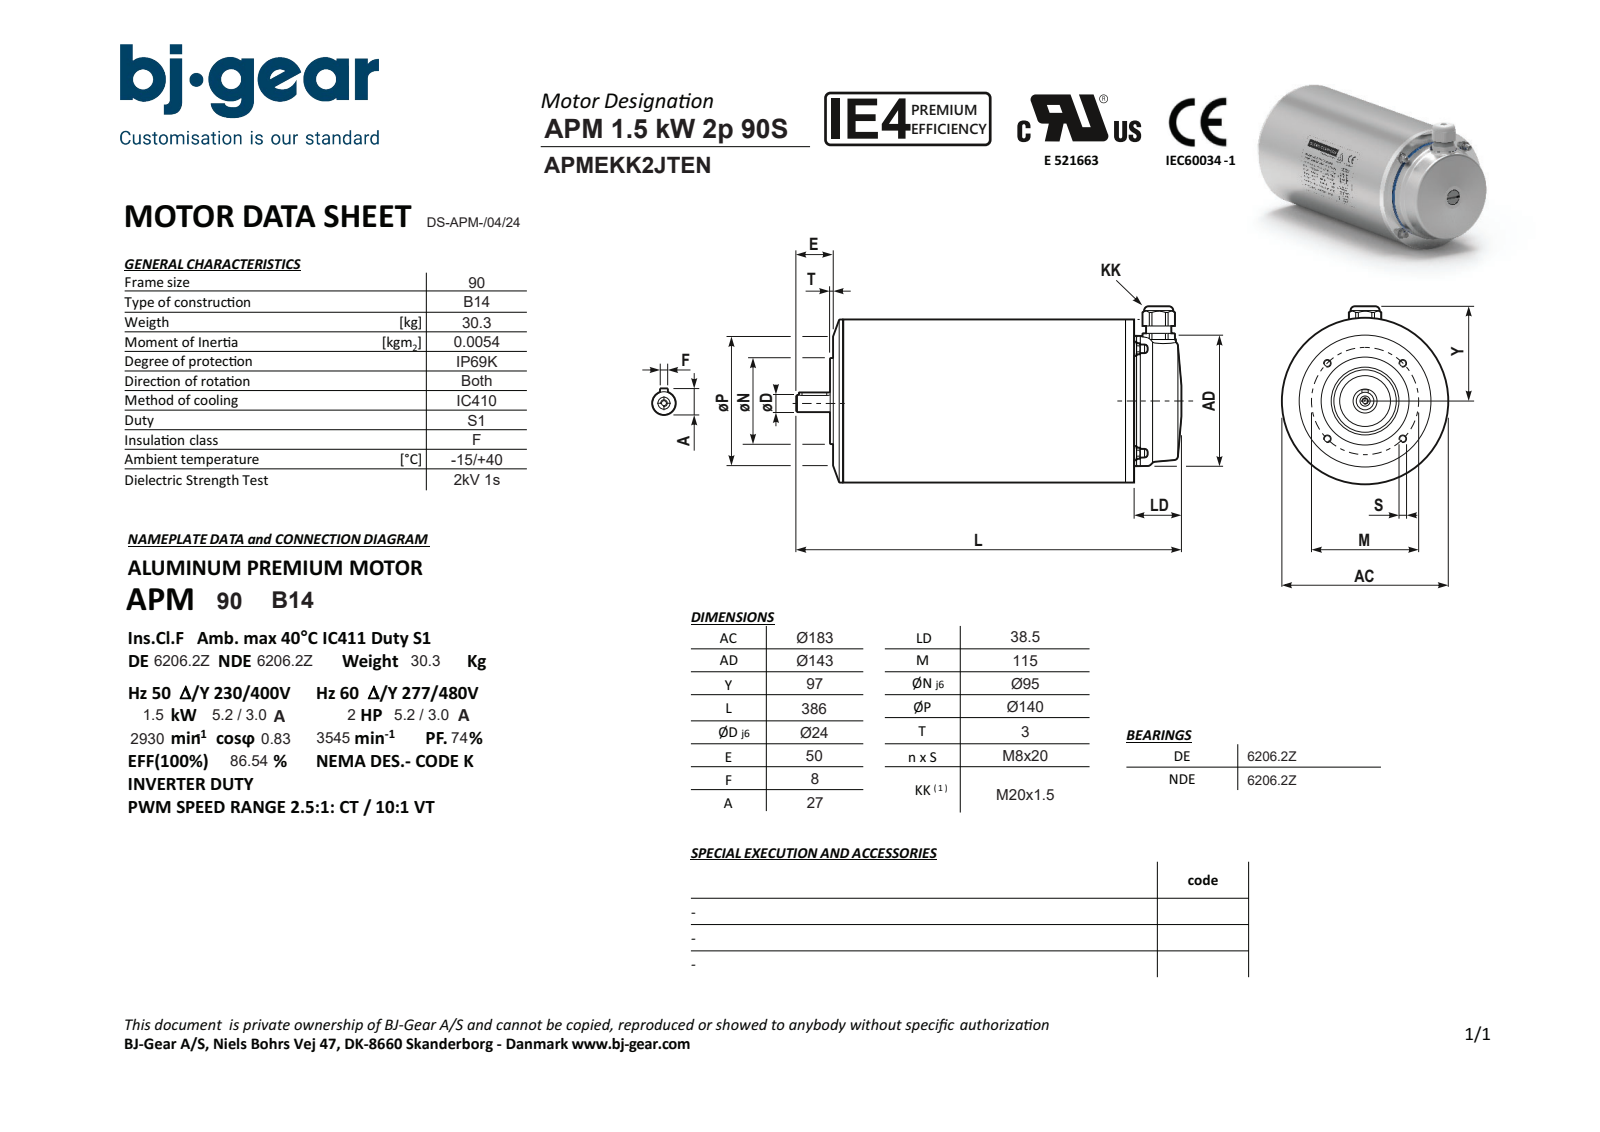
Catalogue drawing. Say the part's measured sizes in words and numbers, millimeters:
The part is named "APMEKK2JTENN4KCR2-N---NNN". Its 3-D file was written by "Solid Edge (AUTOMOTIVE_DESIGN)". It is 1 solid with 156 faces: 75 planar, 50 cylindrical and 31 other. Overall it measures 386 by 187.3 by 182.6 millimeters. Its volume is 8 327 000 cubic millimeters and its surface area 247 972 square millimeters. Round holes: 5 of diameter 6.65, 1 of diameter 8.4, 1 of diameter 16, 1 of diameter 28, 1 of diameter 82. Round bosses or shafts: 4 of diameter 11.5, 4 of diameter 7, 1 of diameter 182.6, 1 of diameter 182.6, 1 of diameter 143, 1 of diameter 95, 1 of diameter 30, 1 of diameter 24. Partial cylindrical surfaces (rounded edges, fillets, slot ends): 2 of radius 4, 1 of radius 13.2. The main face-to-face distances are 297.5, 6, 291.5, 3, 9, 300.5, 8, 336, 38.5, 330. The hole center spacings are 57.5, 81.32, 115.
